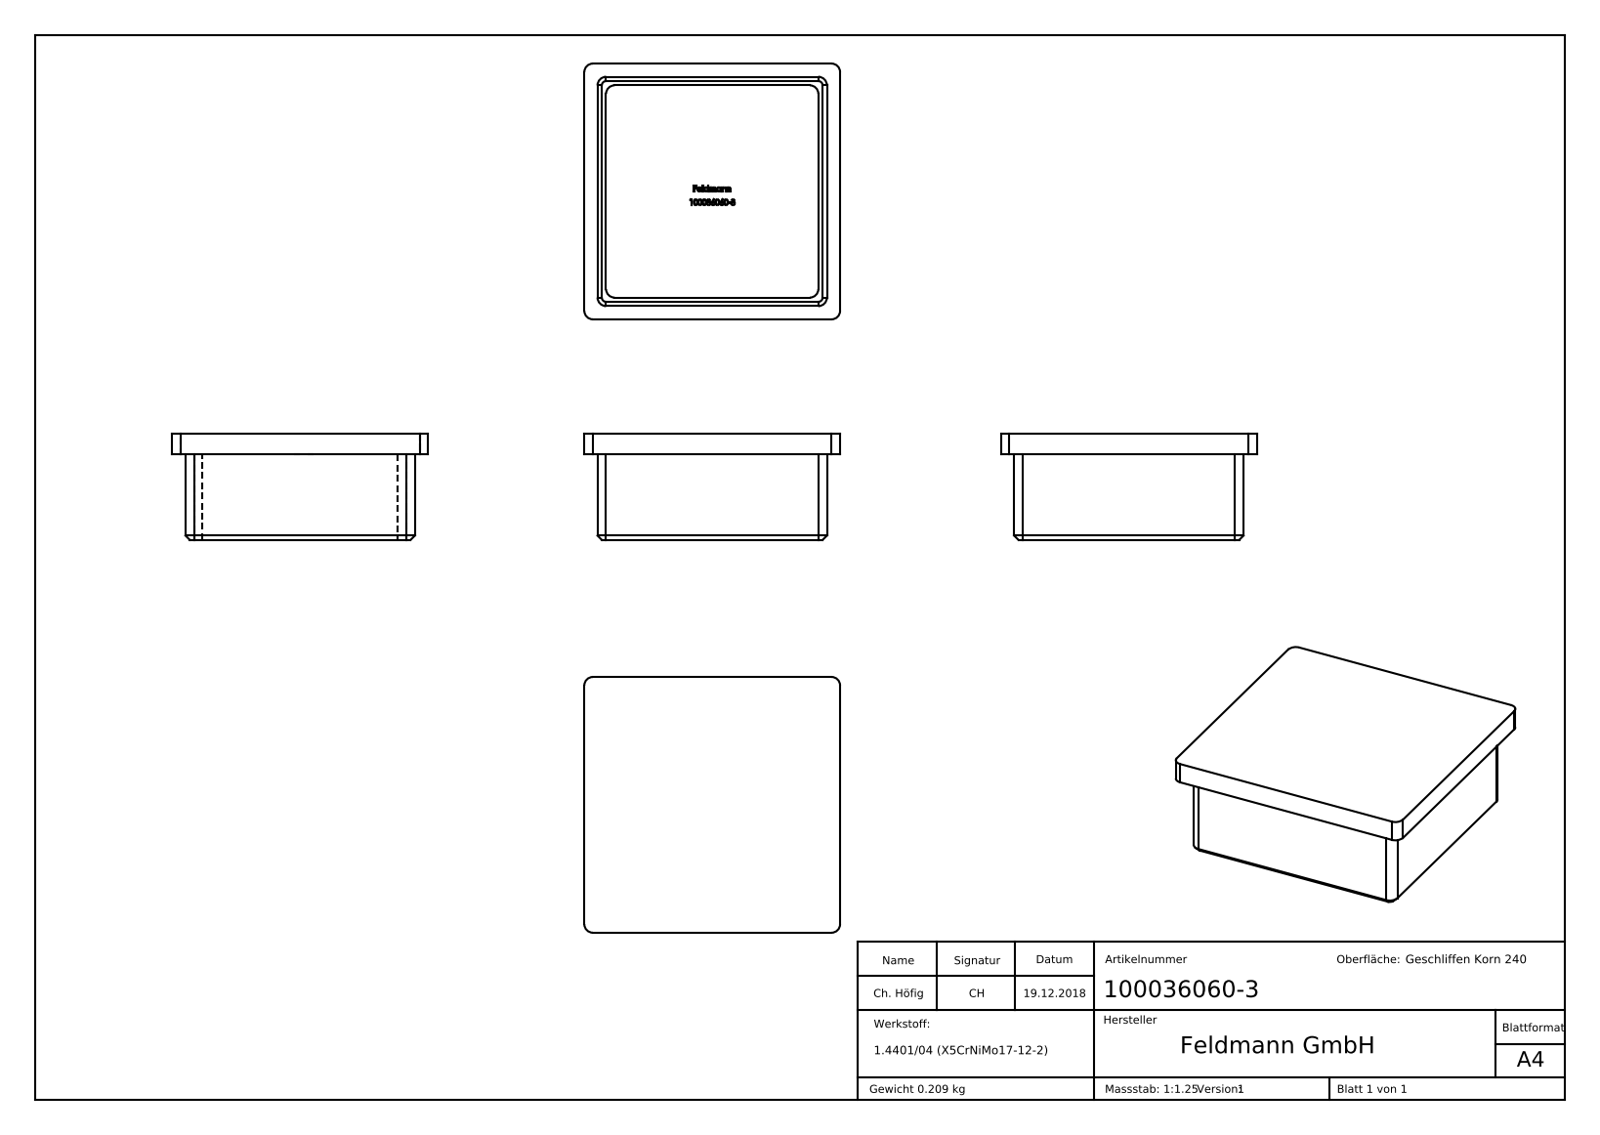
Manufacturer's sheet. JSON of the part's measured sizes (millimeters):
{"part_name": "100036060-3", "step_written_by": "SolidWorks 2015 (CONFIG_CONTROL_DESIGN)", "units": "millimeters", "bodies": {"solids": 1, "faces": 280, "planar": 125, "cylindrical": 12, "other": 143}, "overall_size": [60, 60, 25], "volume_mm3": 26165, "surface_area_mm2": 16412, "partial_cylinders_radius": [[2, 12]], "face_to_face_distances": [2, 51.8, 5, 53.8, 49.8, 3.1, 5.1, 54.9, 56.9, 60]}
